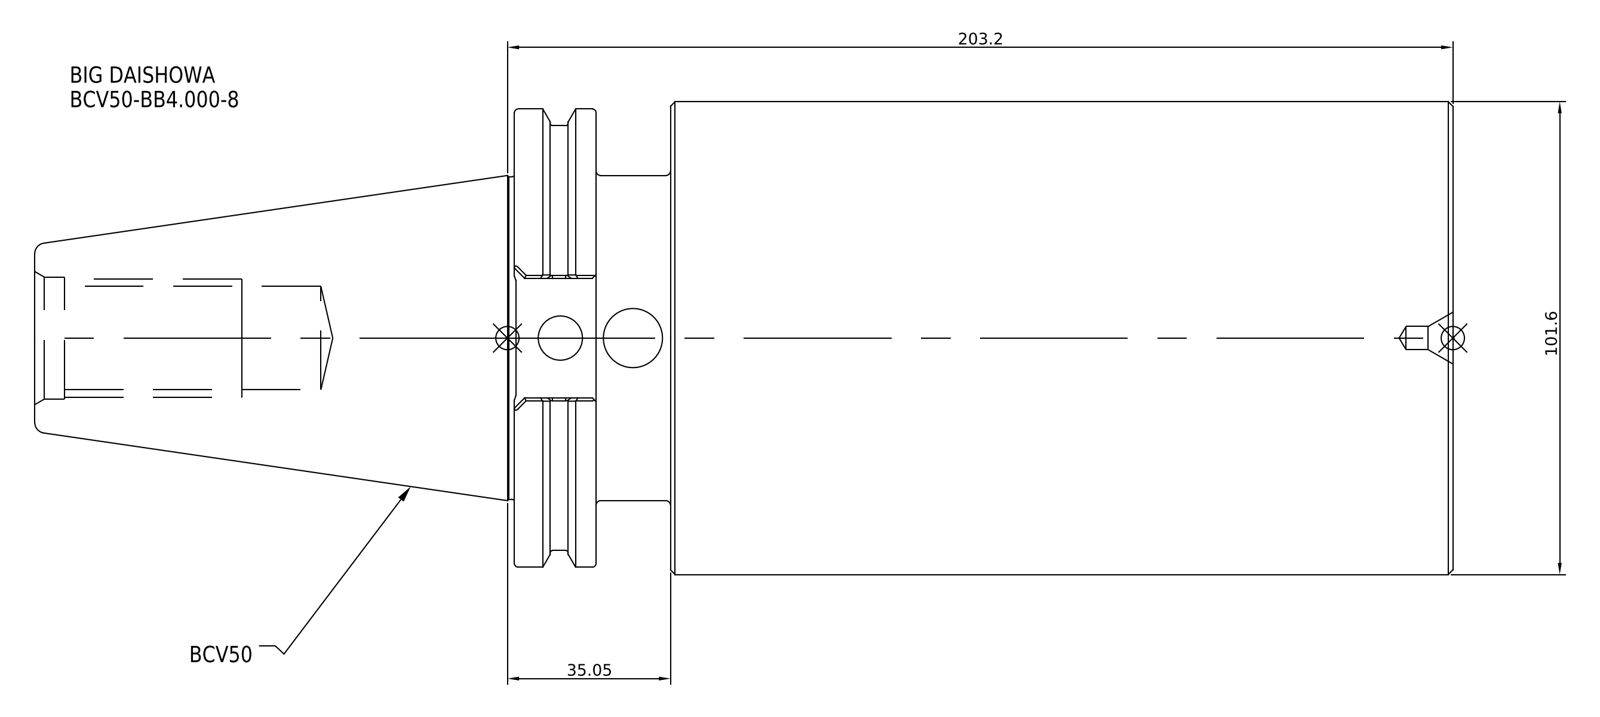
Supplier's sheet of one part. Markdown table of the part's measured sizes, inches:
| quantity | value |
| --- | --- |
| part name | BVC50_BB4_000_8 |
| STEP written by | SolidWorks 2021 (CONFIG_CONTROL_DESIGN) |
| units | inches |
| bodies | 1 solid, 16 faces (7 planar, 6 cylindrical, 3 other) |
| overall size | 12 × 4 × 4 |
| volume | 110.2 in³ |
| surface area | 160 in² |
| round bosses / shafts (diameter × count) | 4 × 1, 3.875 × 1, 3.594 × 1, 2.75 × 1 |
| main face-to-face distances | 6.622, 7.941, 1.319, 7.25, 0.628, 0.691, 12, 5.378, 4.75, 4.059 |
